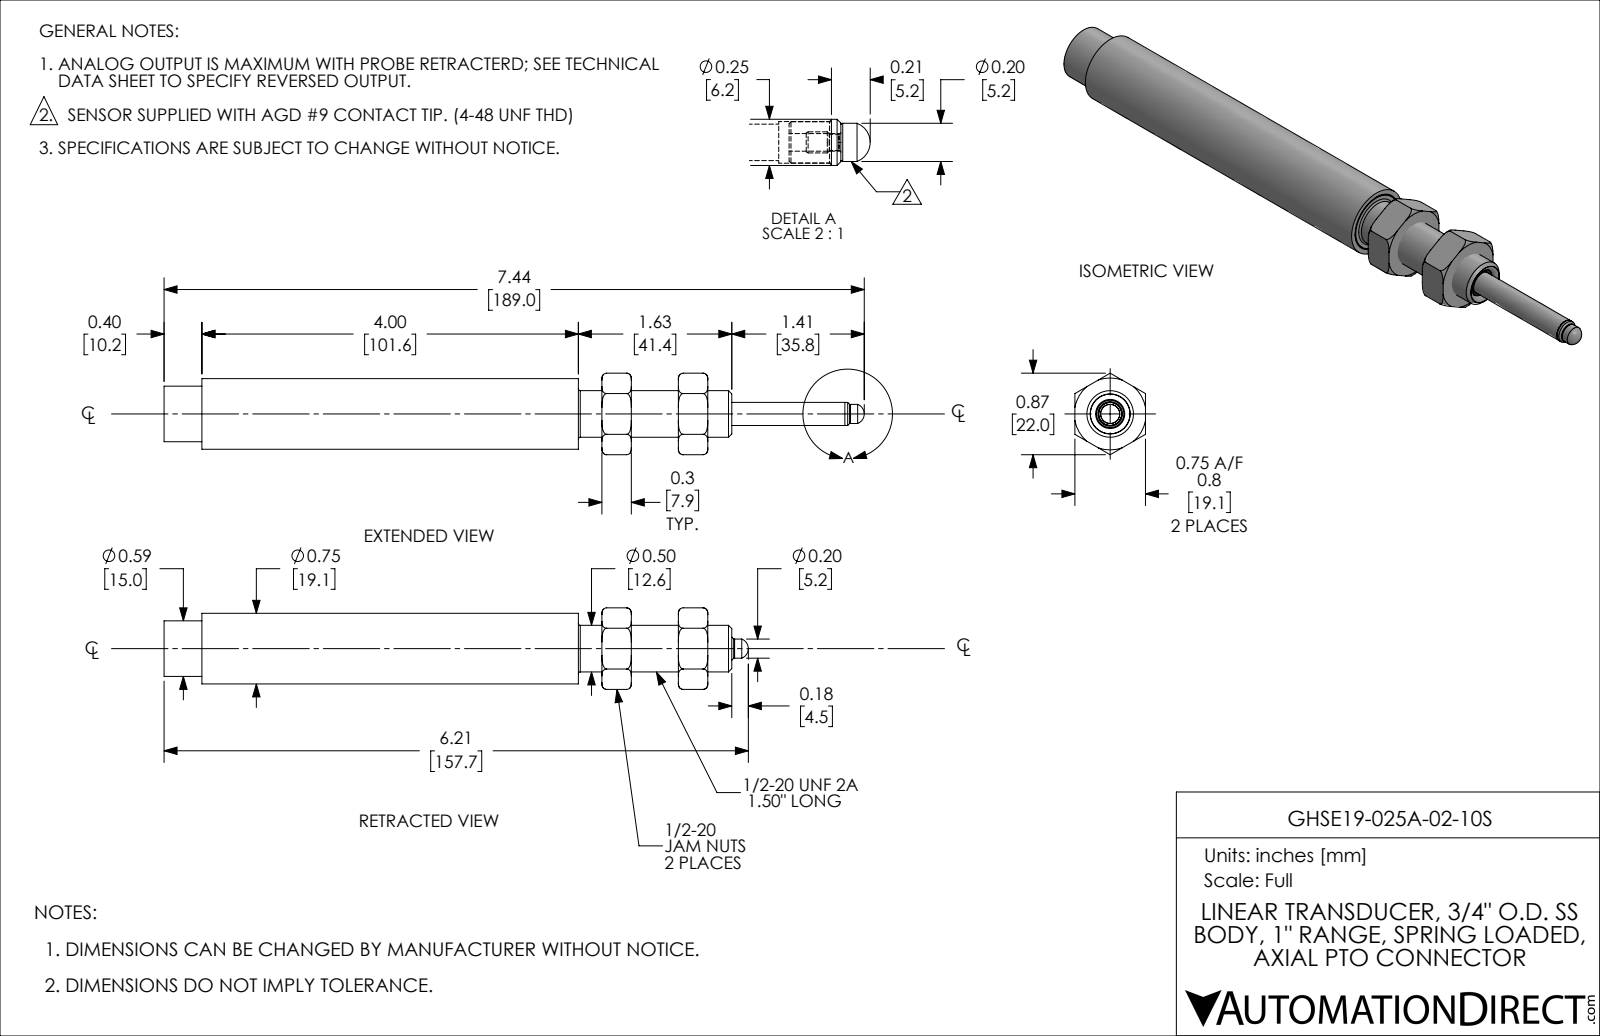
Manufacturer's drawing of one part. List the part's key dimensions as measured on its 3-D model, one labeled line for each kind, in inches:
Part name (STEP PRODUCT): GHSE19-025A-02-10S
STEP written by: SolidWorks 2019 (AUTOMOTIVE_DESIGN)
Units: inches
Bodies: 11 solids, 187 faces (77 planar, 65 cylindrical, 45 other)
Overall size (bounding box): 6.208 × 0.866 × 0.75
Volume: 1.273 in³ · Surface area: 39.45 in²
Round holes (diameter × count): ⌀0.093 ×1, ⌀0.156 ×1, ⌀0.193 ×1, ⌀0.221 ×1, ⌀0.249 ×1, ⌀0.302 ×1, ⌀0.31 ×1, ⌀0.453 ×1, ⌀0.52 ×1, ⌀0.62 ×1, ⌀0.625 ×1, ⌀0.65 ×1
Round bosses / shafts (diameter × count): ⌀0.03 ×6, ⌀0.75 ×1, ⌀0.725 ×1, ⌀0.672 ×1, ⌀0.624 ×1, ⌀0.59 ×1, ⌀0.495 ×1, ⌀0.375 ×1
Partial cylindrical surfaces — rounded edges, fillets, slot ends (radius × count): R0.011 ×2, R0.04 ×2, R0.133 ×1, R0.156 ×1, R0.275 ×1
Main face-to-face distances: 0.75, 0.812, 0.313, 0.813, 1.125, 0.5, 0.312, 0.75, 4.272, 4.585
